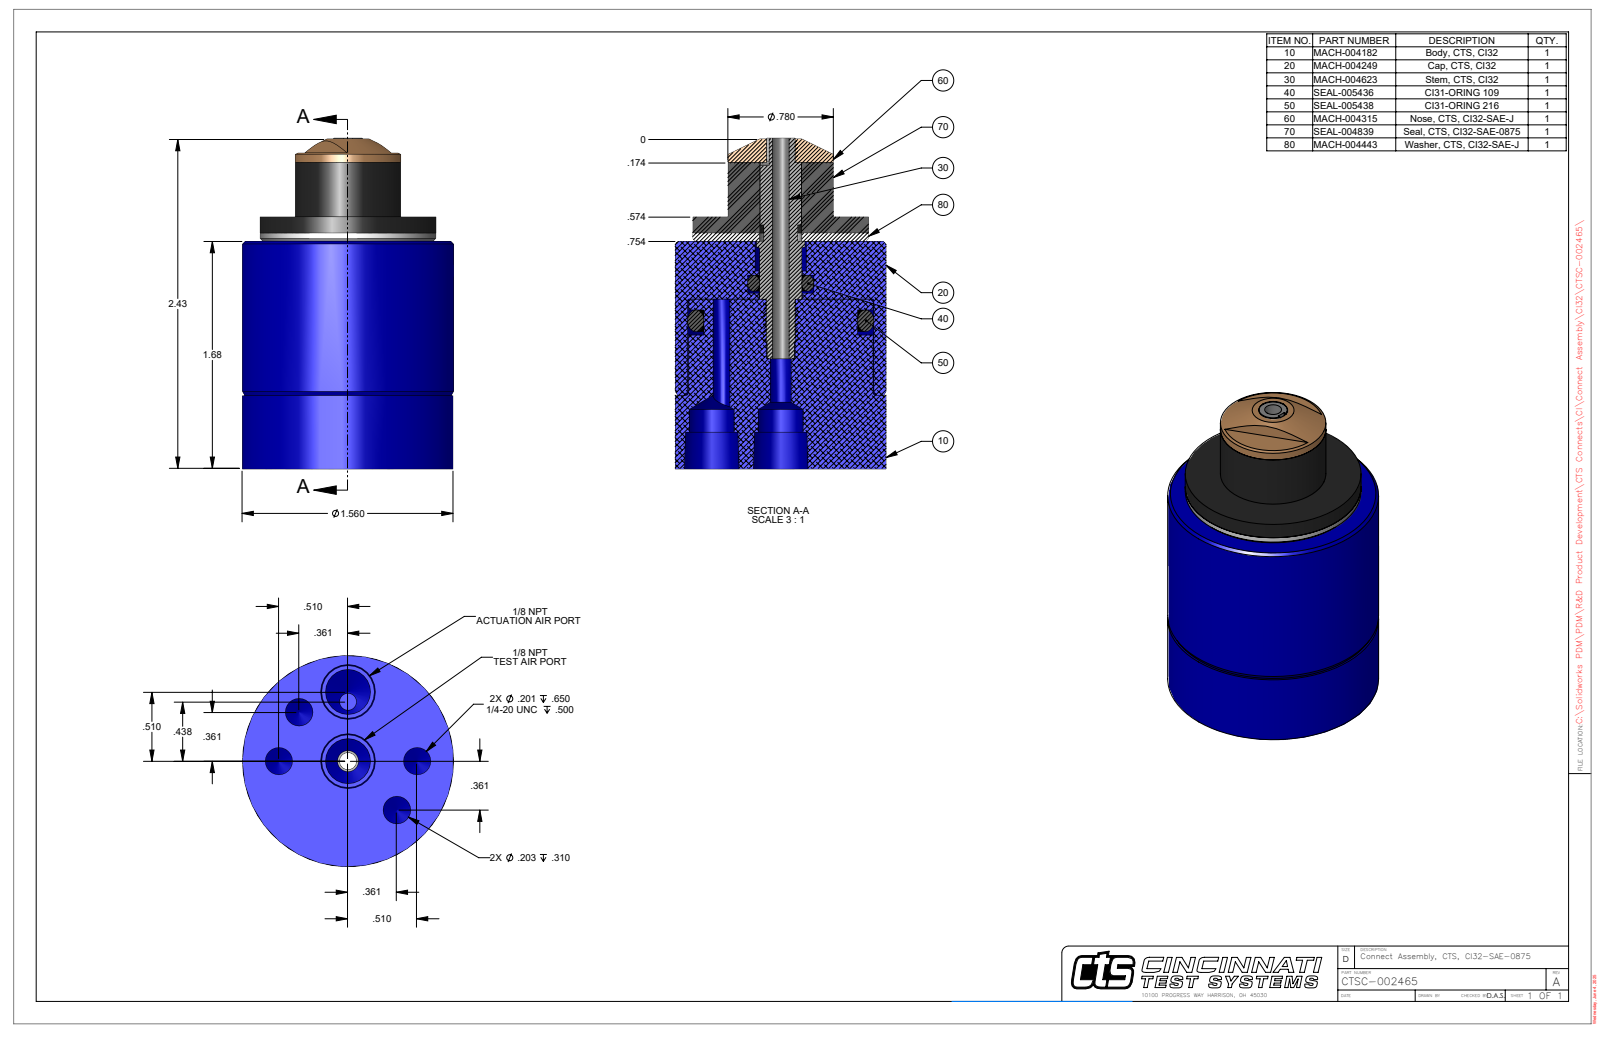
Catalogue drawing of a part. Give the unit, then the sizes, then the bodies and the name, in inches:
Units: inches
Overall size (bounding box): 2.437 × 1.56 × 1.56
Round holes (diameter × count): ⌀0.125 ×2, ⌀0.201 ×2, ⌀0.203 ×2, ⌀0.332 ×2, ⌀0.156 ×1, ⌀0.314 ×1, ⌀0.38 ×1, ⌀1.377 ×1
Round bosses / shafts (diameter × count): ⌀1.56 ×1, ⌀1.365 ×1, ⌀1.3 ×1, ⌀0.78 ×1, ⌀0.357 ×1, ⌀0.31 ×1
Partial cylindrical surfaces — rounded edges, fillets, slot ends (radius × count): R0.106 ×1
Main face-to-face distances: 1.857, 1.677, 0.18, 2.327, 0.65, 0.47, 0.542, 1.135, 1.315, 1.785
Hole centre spacings: 0.51, 0.39, 0.942, 0.672, 0.721, 0.072, 0.369, 0.437
Volume: 3.48 in³ · Surface area: 19.95 in²
Bodies: 1 solid, 102 faces (29 planar, 39 cylindrical, 34 other)
Part name (STEP PRODUCT): CTSC-002465
STEP written by: SolidWorks 2023 (AUTOMOTIVE_DESIGN)
